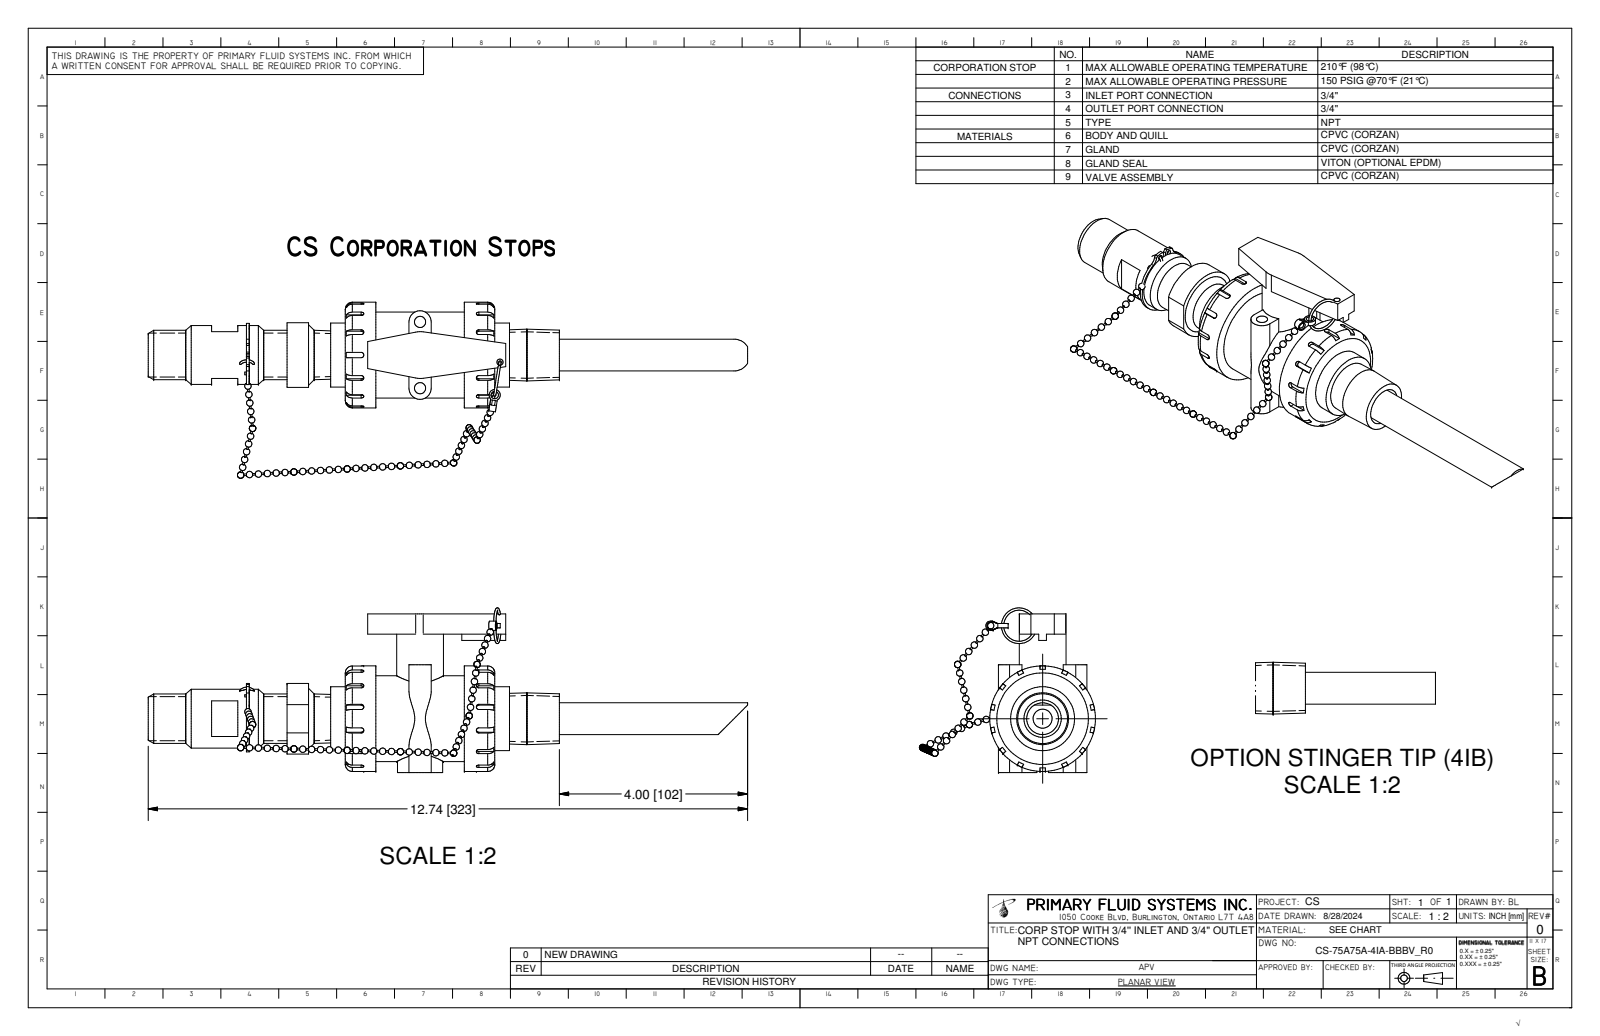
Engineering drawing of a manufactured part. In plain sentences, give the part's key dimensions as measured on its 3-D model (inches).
Its 3-D file was written by "Autodesk Inventor 2025 (CONFIG_CONTROL_DESIGN)". It is 19 solids with 416 faces: 204 planar, 133 cylindrical and 79 other. Overall it measures 12.735 by 3.739 by 3.499 inches. Its volume is 18.43 cubic inches and its surface area 123.2 square inches. Round holes: 2 of diameter 0.098, 2 of diameter 0.15, 2 of diameter 0.157, 2 of diameter 0.236, 1 of diameter 0.13, 1 of diameter 0.403, 1 of diameter 0.423, 1 of diameter 0.697, 1 of diameter 0.744, 1 of diameter 0.793, 1 of diameter 0.803, 1 of diameter 1.05. Round bosses or shafts: 9 of diameter 0.035, 2 of diameter 0.236, 1 of diameter 2.244, 1 of diameter 1.823, 1 of diameter 1.358, 1 of diameter 1.343, 1 of diameter 1.25, 1 of diameter 1.14. Partial cylindrical surfaces (rounded edges, fillets, slot ends): 26 of radius 0.056, 2 of radius 0.054, 2 of radius 0.098, 2 of radius 0.197, 2 of radius 0.236, 1 of radius 0.75, 1 of radius 0.752. The main face-to-face distances are 0.647, 2.529, 0.656, 2.537, 3.184, 0.312, 0.959, 2.841, 3.487, 3.176. The hole center spacings are 0.658, 0.704, 0.252, 0.314, 0.51, 0.512, 0.708, 1.408.
